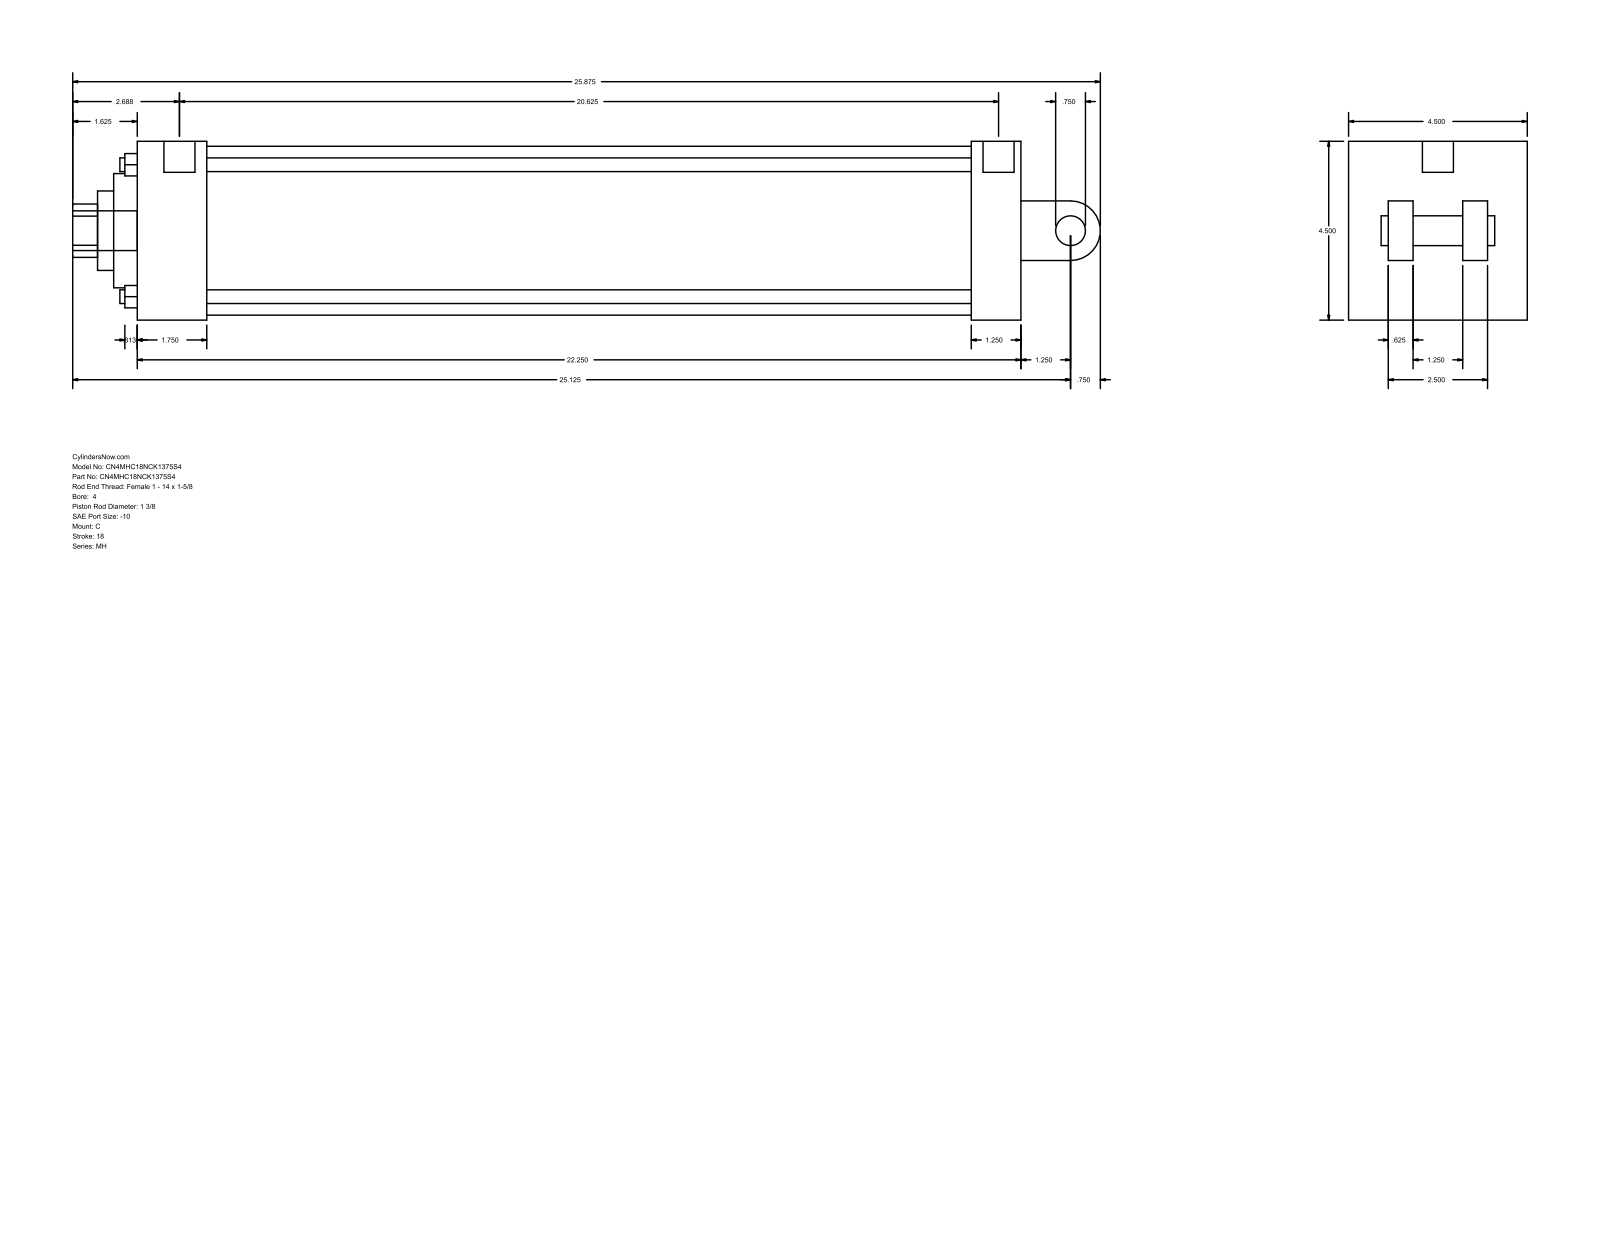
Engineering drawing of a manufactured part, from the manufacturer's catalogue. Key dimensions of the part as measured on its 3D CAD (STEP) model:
Part name (STEP PRODUCT): MH_C__0400_1.375
STEP written by: GSSL Pune (CONFIG_CONTROL_DESIGN)
Units: millimetres
Bodies: 0 solids, 101 faces (71 planar, 30 cylindrical, 0 other)
Overall size (bounding box): 657.23 × 114.3 × 114.3
Round holes (diameter × count): ⌀8.76 ×4, ⌀8.73 ×2, ⌀19.84 ×1, ⌀34.92 ×1, ⌀50.8 ×1, ⌀73.03 ×1, ⌀107.95 ×1
Round bosses / shafts (diameter × count): ⌀8.73 ×2, ⌀25.4 ×1, ⌀19.84 ×1, ⌀19.05 ×1
Partial cylindrical surfaces — rounded edges, fillets, slot ends (radius × count): R17.06 ×1, R19.05 ×1
Main face-to-face distances: 114.3, 565.15, 44.45, 533.4, 488.95, 520.7, 31.75, 73.03, 41.27, 38.1
Hole centre spacings: 59.62, 84.32, 119.25, 1.59
